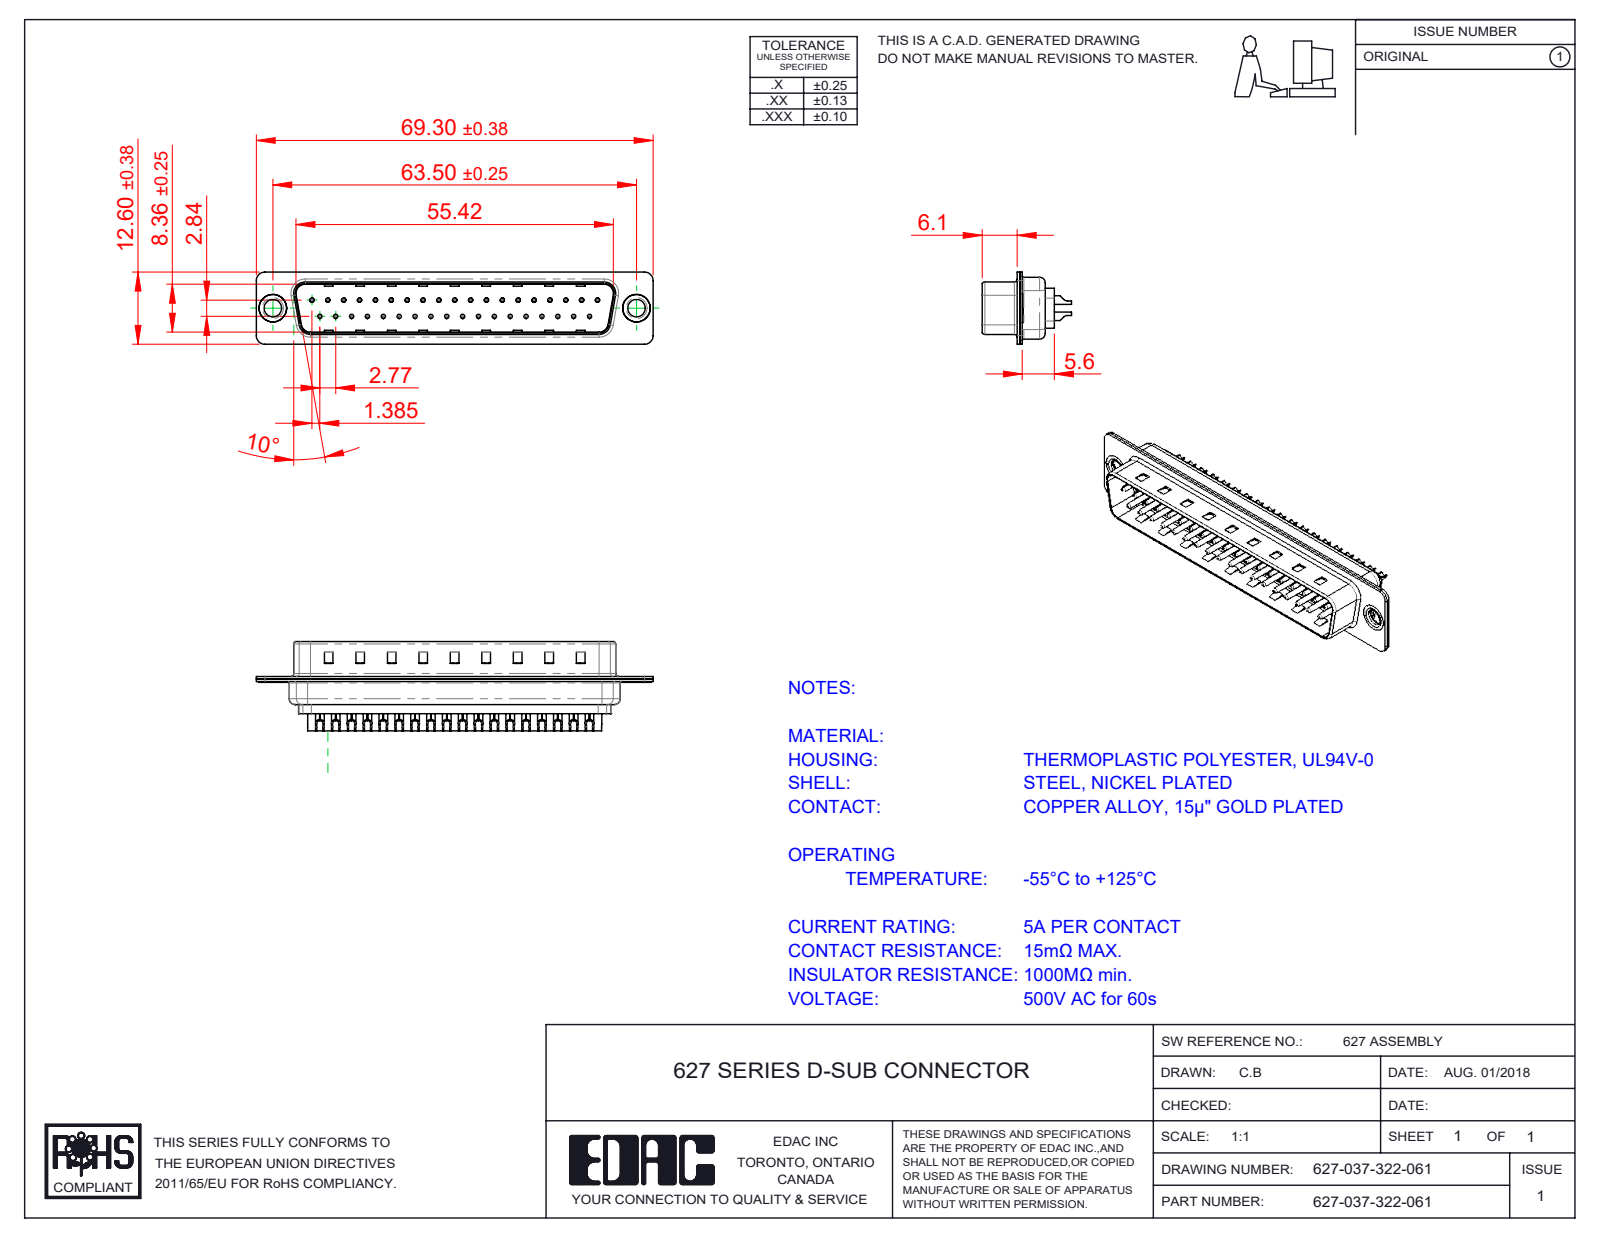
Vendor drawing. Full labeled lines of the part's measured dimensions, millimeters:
Part name (STEP PRODUCT): 627 Shell Rear_37 Contacts; 627 Shell Front_37 Contacts; 627 Contact Row 2_22L; 627 Housing_37 LP (+3 more)
STEP written by: SolidWorks 2020 (CONFIG_CONTROL_DESIGN)
Units: millimetres
Bodies: 42 solids, 2754 faces (721 planar, 1198 cylindrical, 835 other)
Overall size (bounding box): 69.3 × 15.35 × 12.6
Volume: 3 636 mm³ · Surface area: 10 612 mm²
Round holes (diameter × count): ⌀0.35 ×37, ⌀1.1 ×37, ⌀1.6 ×37, ⌀3.05 ×2, ⌀4 ×2, ⌀4.8 ×2
Round bosses / shafts (diameter × count): ⌀2 ×37, ⌀1.5 ×37, ⌀0.75 ×37, ⌀5 ×2, ⌀4.9 ×2, ⌀3.55 ×2
Partial cylindrical surfaces — rounded edges, fillets, slot ends (radius × count): R1.5 ×16, R2 ×12, R0.5 ×8, R1.6 ×8, R1 ×6, R0.25 ×4, R0.6 ×4, R0.65 ×4
Main face-to-face distances: 0.4, 0.82, 9.58, 0.45, 8.76, 0.9, 1.5, 1.4, 6.05, 0.5
Hole centre spacings: 3.16, 2.77, 5.54, 8.31, 5.04, 10.1, 11.08, 12.78
